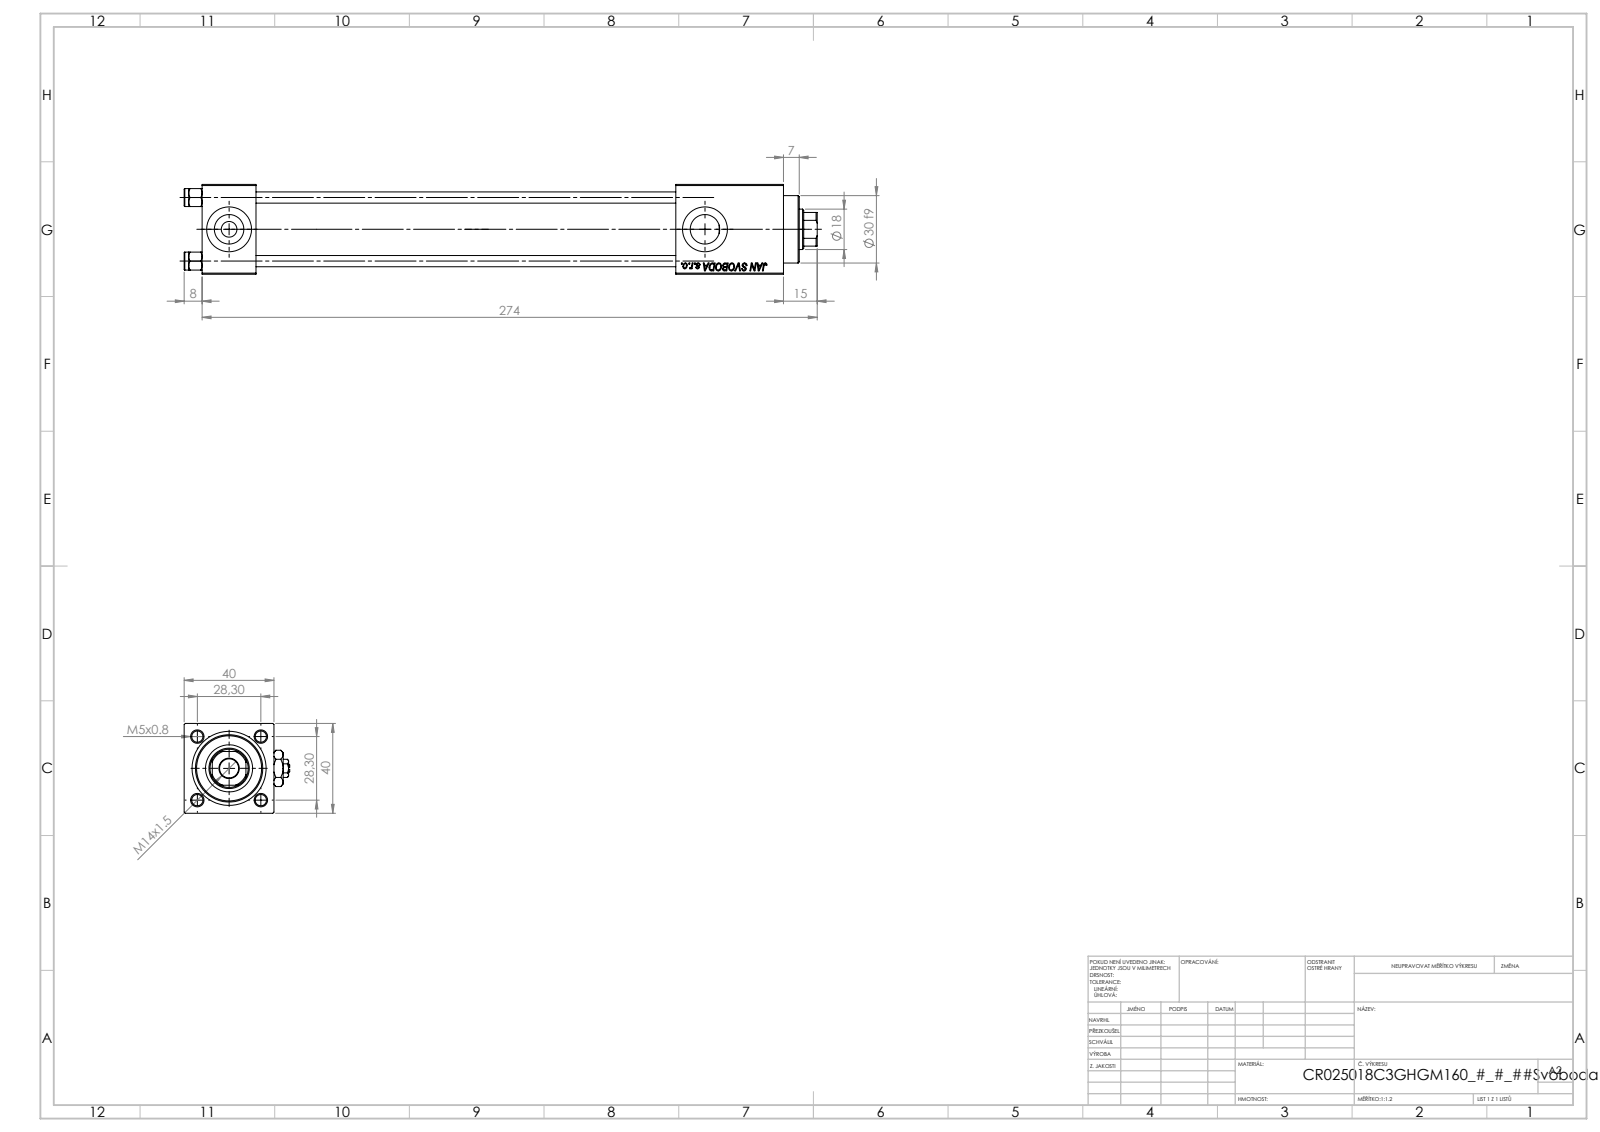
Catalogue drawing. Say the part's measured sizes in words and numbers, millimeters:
The part is named "V215CR_VCP_C; V215_VC_A; Zatka_pro_OIL_PORT; V215CR_C_TYCINKA (+2 more)". Its 3-D file was written by "SolidWorks 2019 (CONFIG_CONTROL_DESIGN)". It is 13 solids with 1245 faces: 571 planar, 96 cylindrical and 578 other. Overall it measures 282 by 47 by 40 millimeters. Its volume is 232 159 cubic millimeters and its surface area 99 828 square millimeters. Round holes: 4 of diameter 5, 3 of diameter 20, 2 of diameter 7, 2 of diameter 13.16, 1 of diameter 8.5, 1 of diameter 18, 1 of diameter 21, 1 of diameter 25, 1 of diameter 30. Round bosses or shafts: 4 of diameter 8, 1 of diameter 31. Partial cylindrical surfaces (rounded edges, fillets, slot ends): 1 of radius 8.5. The main face-to-face distances are 40, 24, 39.8, 211, 187, 230.3, 206.3, 19.3, 48, 259. The hole center spacings are 20.01, 28.3, 40.02, 212.
